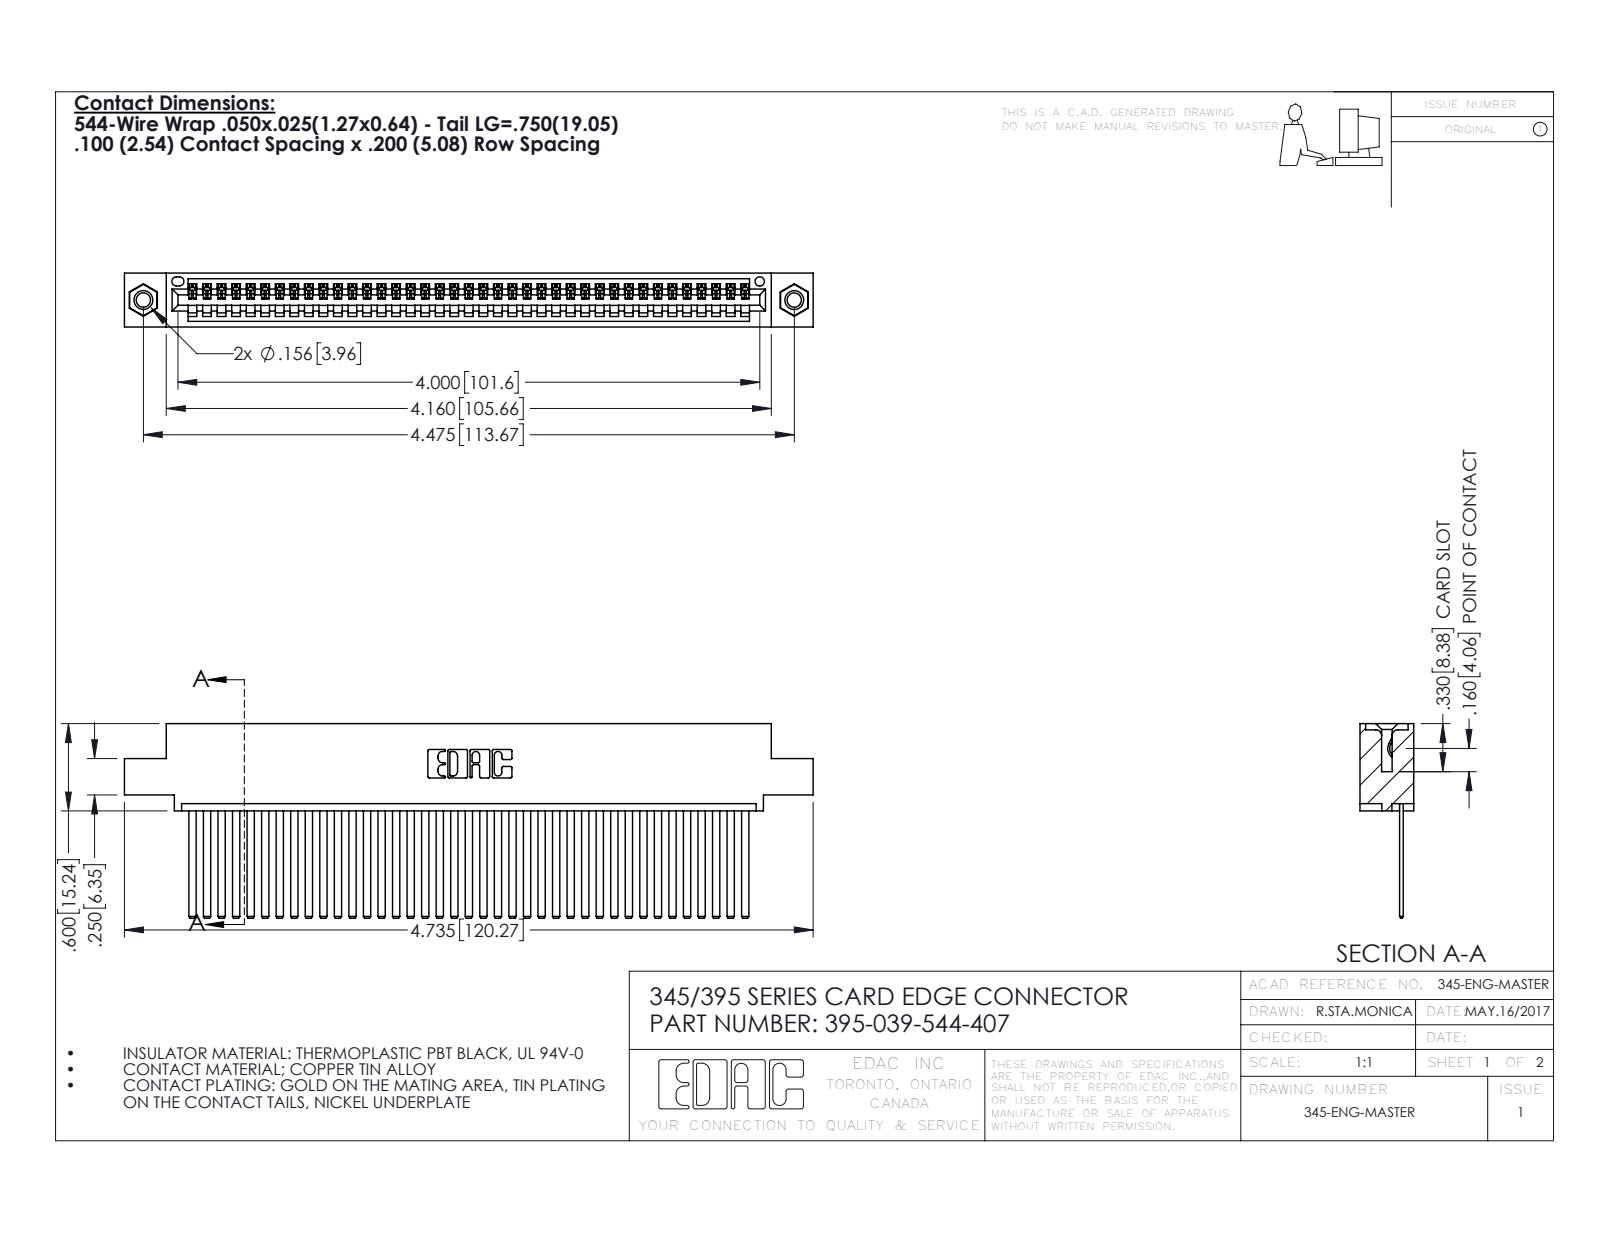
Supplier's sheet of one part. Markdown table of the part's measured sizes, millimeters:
| quantity | value |
| --- | --- |
| part name | 345 Part_0.110 Offset - 0.156 Dia-TI; 395-039-544-407; 345-250-001_345-250-005-103; 345-292-001_345-293-144 |
| STEP written by | SolidWorks 2016 (CONFIG_CONTROL_DESIGN) |
| units | millimeters |
| bodies | 42 solids, 2218 faces (1520 planar, 682 cylindrical, 16 other) |
| overall size | 120.3 × 34 × 9.4 |
| volume | 11 800 mm³ |
| surface area | 17 060 mm² |
| round holes (diameter × count) | 2.5 × 2, 3.2 × 2, 4 × 2, 1.6 × 1 |
| round bosses / shafts (diameter × count) | 3.9 × 2 |
| partial cylindrical surfaces (radius × count) | 0.2 × 78, 0.3 × 22, 0.2 × 6, 0.8 × 6, 0.7 × 3, 0.8 × 2, 1 × 2, 0.4 × 1 |
| main face-to-face distances | 1.8, 7.6, 0.6, 2.5, 6.9, 9.4, 5.1, 5.7, 3.8, 1.8 |
| hole center spacings | 6.9, 107.7, 113.7 |
